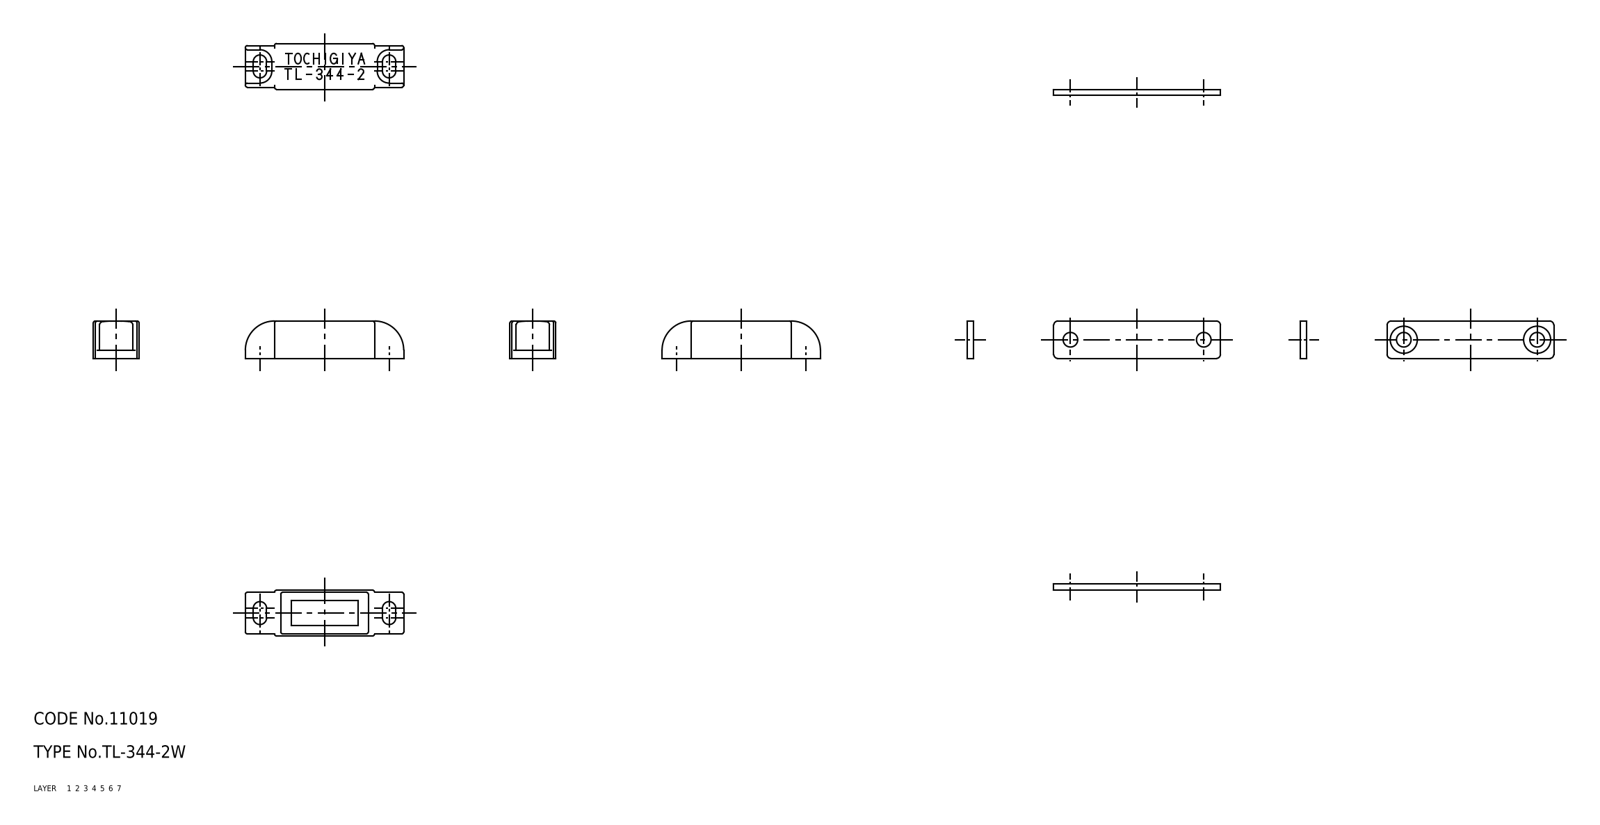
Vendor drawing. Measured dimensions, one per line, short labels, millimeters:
name: 67113916; 67113929; 67113942
written by: CADfix (AUTOMOTIVE_DESIGN)
unit: mm
bodies: 3 solids, 97 faces (0 planar, 0 cylindrical, 97 other)
size: 40 × 24.5 × 9
volume: 3 337 mm³; area: 3 238 mm²
